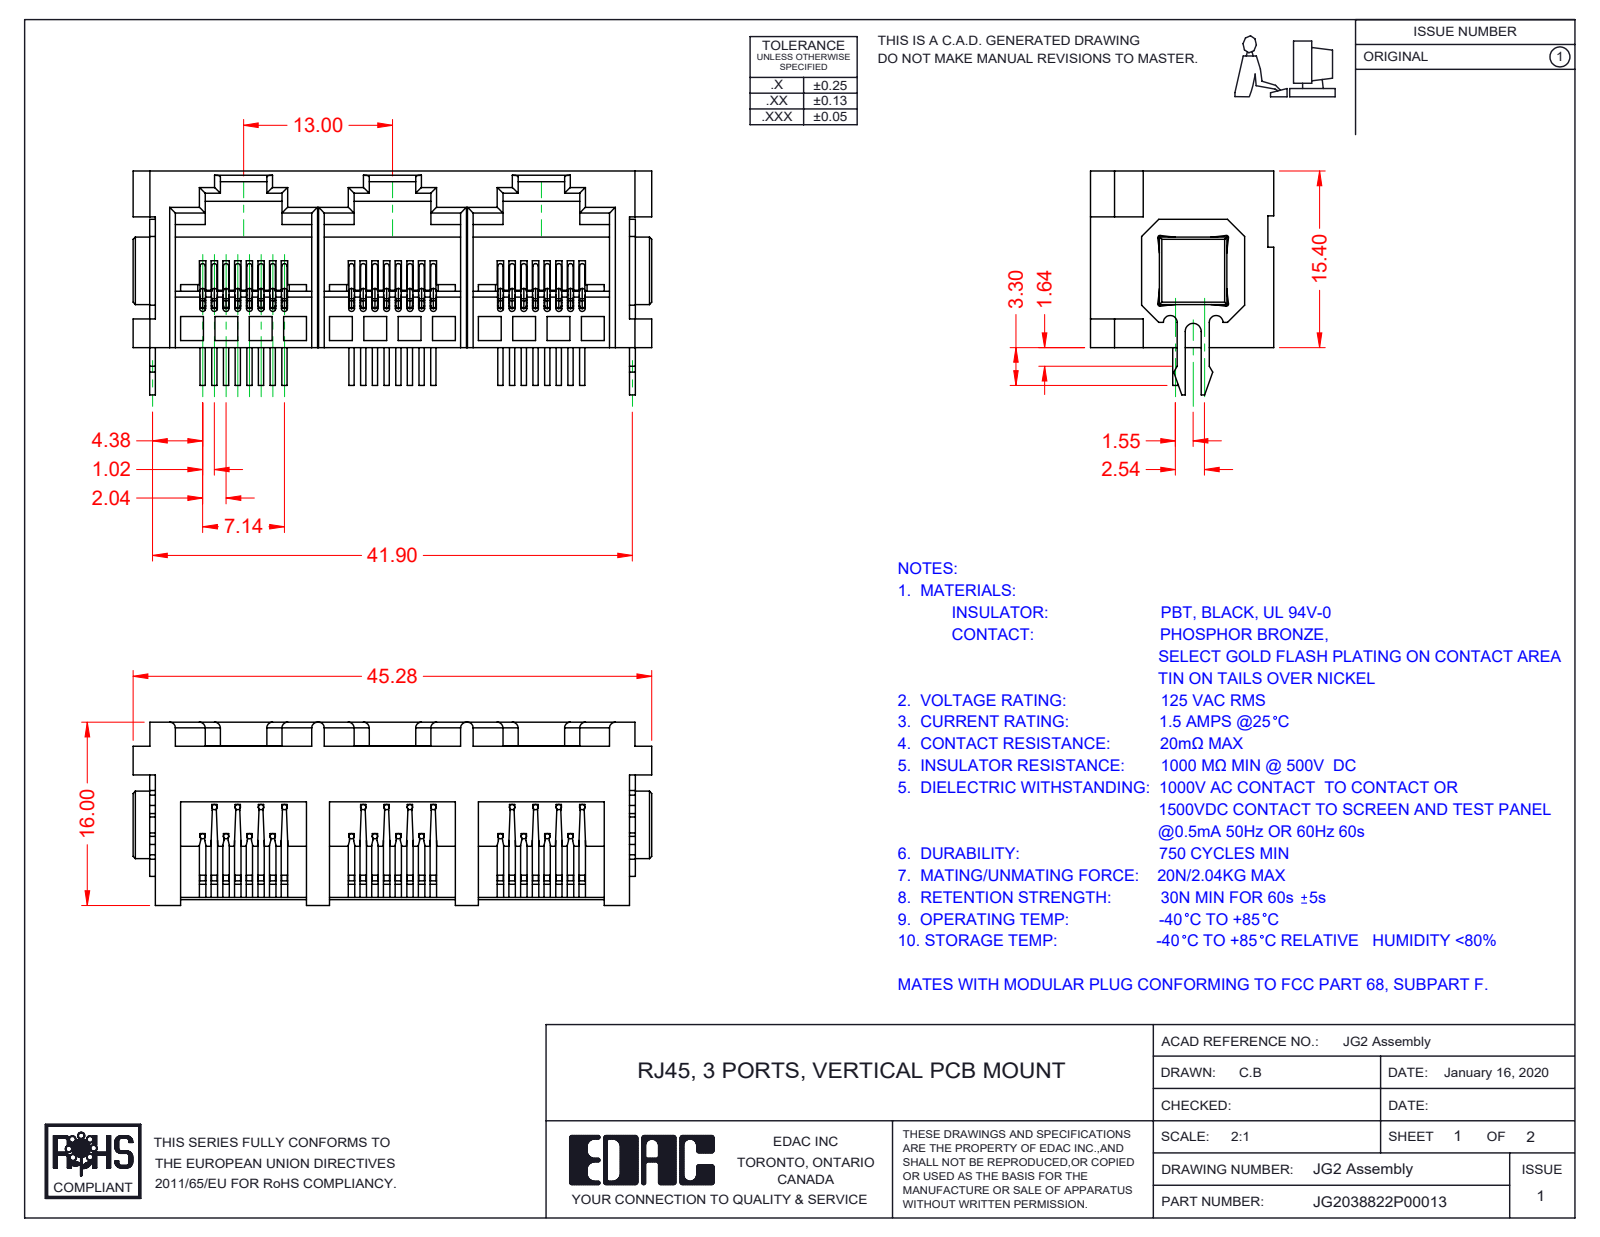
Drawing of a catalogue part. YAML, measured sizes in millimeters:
part_name: "G2 Contacts; G2 Boardlock1; G2 Boardlock2; G2 Insulator (+2 more)"
step_written_by: "SolidWorks 2016 (CONFIG_CONTROL_DESIGN)"
units: millimeters
bodies: {solids: 30, faces: 1835, planar: 1210, cylindrical: 457, other: 168}
overall_size: [45.28, 19.54, 16]
volume: 4876
surface_area: 9571
round_bosses_or_shafts:
  - {diameter: 0.46, count: 96}
partial_cylinders:
  - {radius: 0.5, count: 69}
  - {radius: 0.2, count: 4}
  - {radius: 20.35, count: 4}
  - {radius: 0.3, count: 3}
  - {radius: 0.6, count: 2}
  - {radius: 0.21, count: 1}
  - {radius: 0.45, count: 1}
  - {radius: 0.7, count: 1}
face_to_face_distances: [13, 12, 0.5, 3.4, 2.2, 11.08, 0.92, 26, 11, 2]
